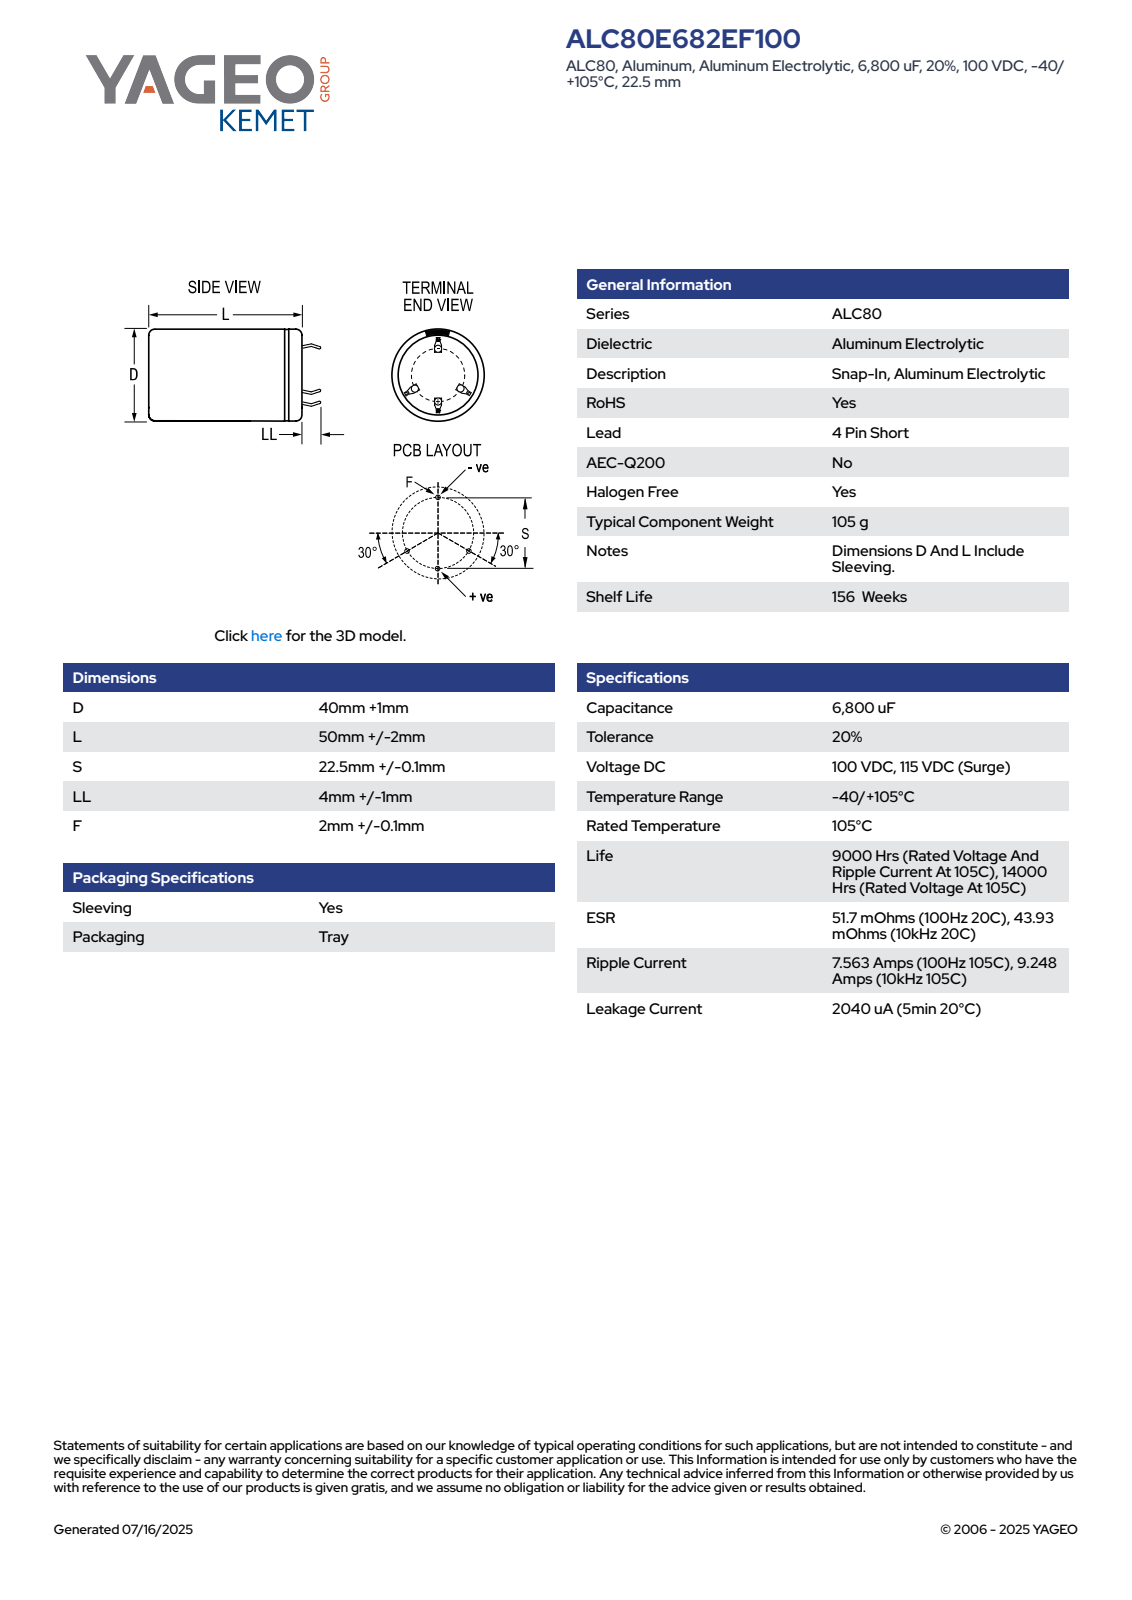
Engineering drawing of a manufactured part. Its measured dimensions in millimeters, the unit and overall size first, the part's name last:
Units: millimetres
Overall size (bounding box): 56.99 × 41 × 41
Round holes (diameter × count): ⌀36.28 ×1
Round bosses / shafts (diameter × count): ⌀41 ×1
Partial cylindrical surfaces — rounded edges, fillets, slot ends (radius × count): R20.49 ×1
Main face-to-face distances: 51.99, 52.49, 0.5, 0.6, 15.16, 0.75, 1.35, 15.46, 14.86, 2.1
Volume: 67 878 mm³ · Surface area: 9 366 mm²
Bodies: 1 solid, 134 faces (80 planar, 15 cylindrical, 39 other)
Part name (STEP PRODUCT): CARS_K4P_40X50_D41L52S22.5LL5F2.1
STEP written by: SolidWorks 2014 (AUTOMOTIVE_DESIGN)
